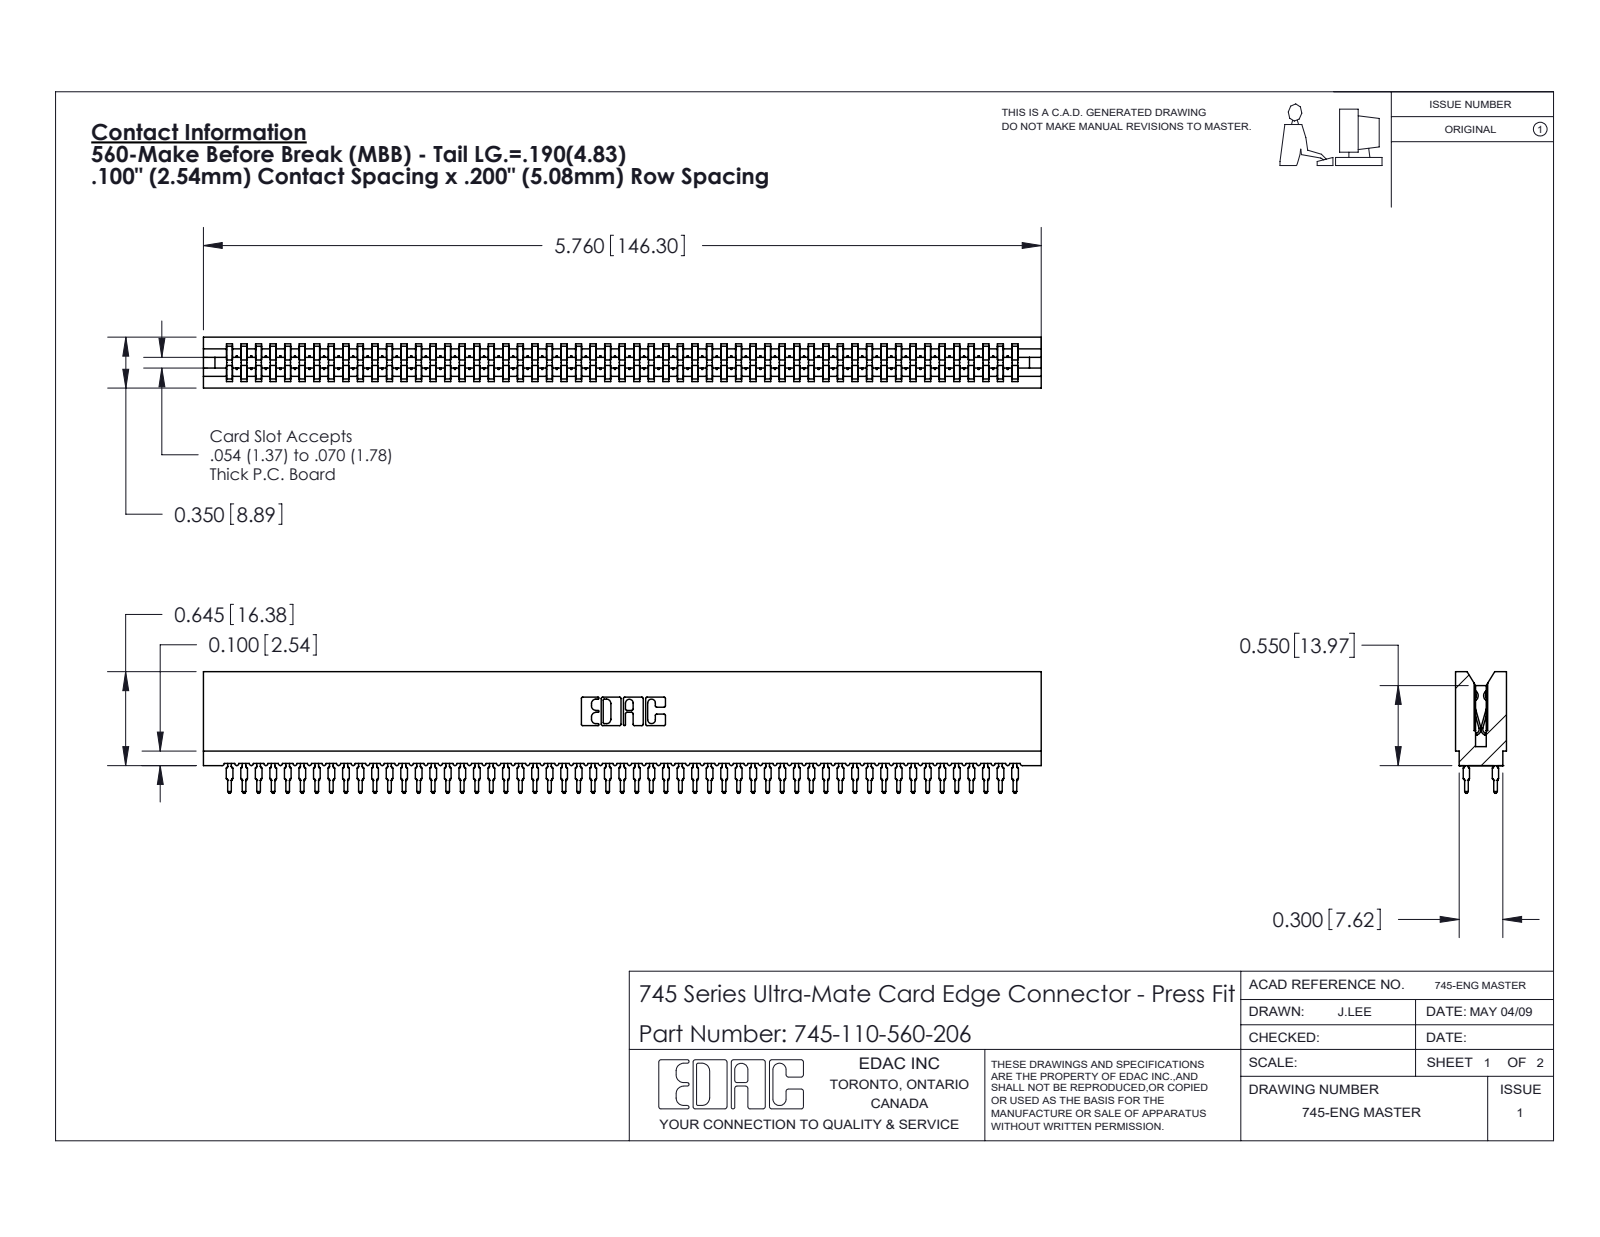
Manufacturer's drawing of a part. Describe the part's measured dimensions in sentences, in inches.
The part is named "745-110-560-206; 745-292-001_560; 745 Part_Insulator Option - 06". Its 3-D file was written by "SolidWorks 2020 (CONFIG_CONTROL_DESIGN)". It is 111 solids with 10931 faces: 5666 planar, 2405 cylindrical and 2860 other. Overall it measures 5.76 by 0.836 by 0.35 inches. Its volume is 0.823 cubic inches and its surface area 45.68 square inches. Partial cylindrical surfaces (rounded edges, fillets, slot ends): 220 of radius 0.021, 110 of radius 0.015, 22 of radius 0.01, 8 of radius 0.005, 8 of radius 0.011, 6 of radius 0.007, 6 of radius 0.031, 3 of radius 0.026. The main face-to-face distances are 0.35, 0.063, 0.287, 0.2, 0.045, 0.305, 0.018, 0.243, 0.138, 0.212.
